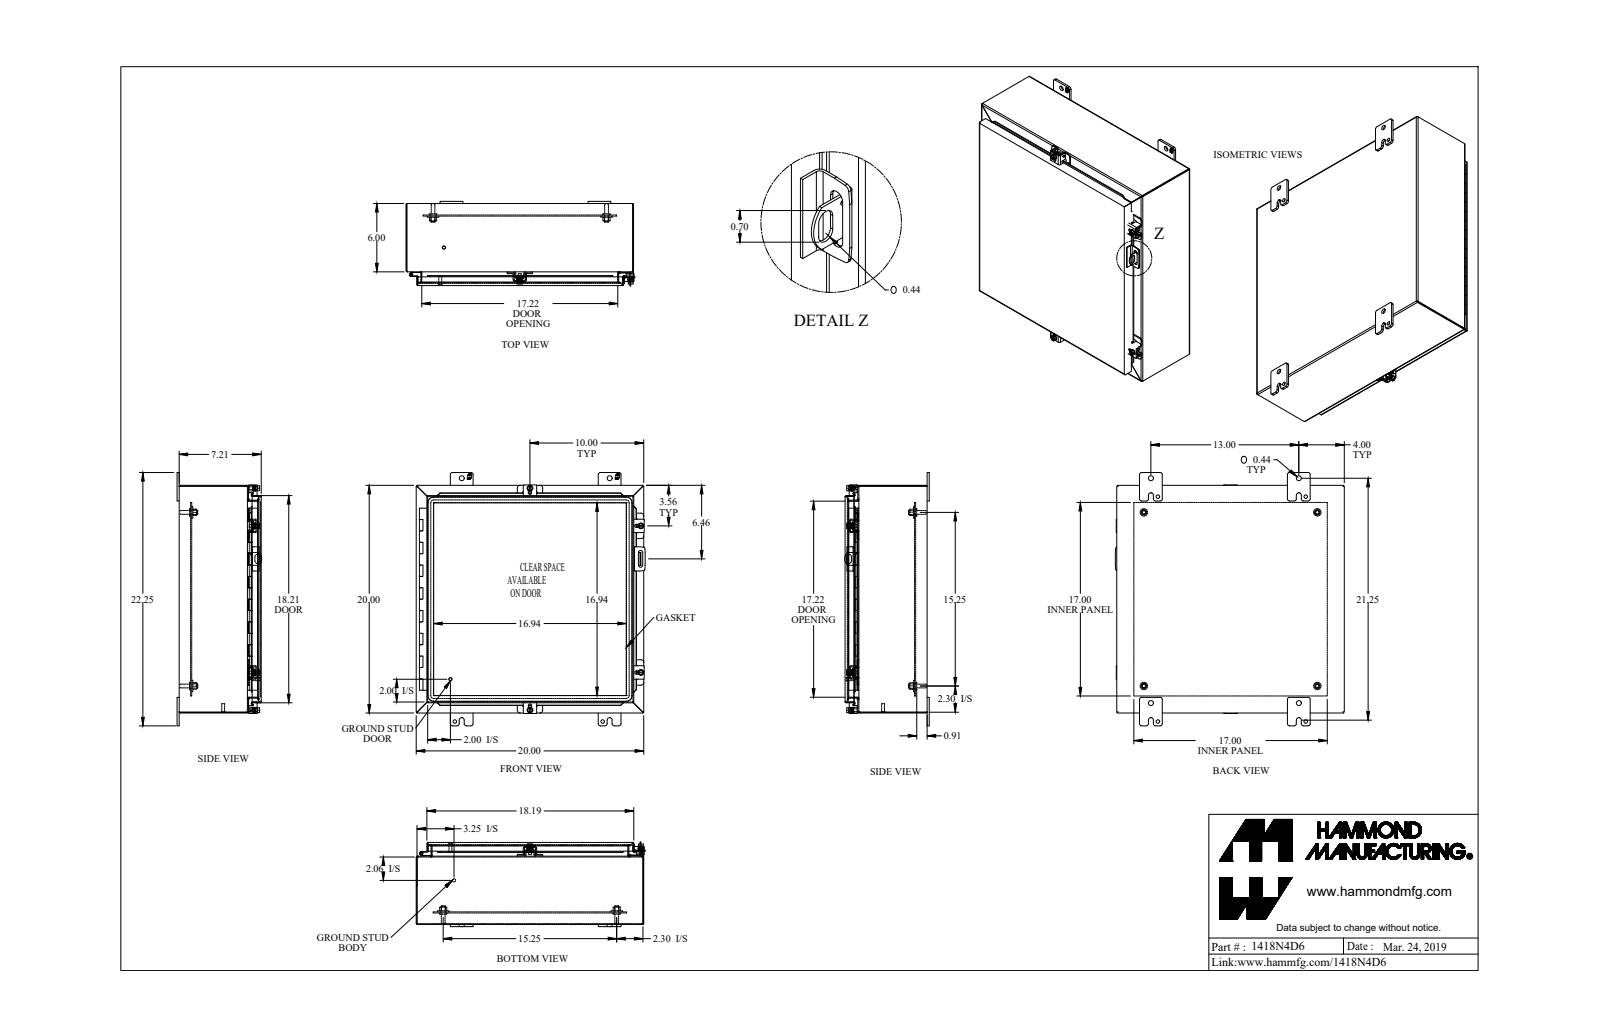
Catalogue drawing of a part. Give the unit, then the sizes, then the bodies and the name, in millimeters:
Units: millimetres
Overall size (bounding box): 565.2 × 511.2 × 188.9
Round holes (diameter × count): ⌀5.4 ×4, ⌀6.7 ×4, ⌀8 ×4, ⌀9.5 ×4, ⌀11.1 ×4, ⌀12.7 ×4, ⌀7.8 ×2, ⌀11.3 ×2, ⌀3.2 ×1, ⌀4.7 ×1
Round bosses / shafts (diameter × count): ⌀16.5 ×4, ⌀12.7 ×4, ⌀9.9 ×4, ⌀9.5 ×4, ⌀8.4 ×4, ⌀6.2 ×4, ⌀25.4 ×2, ⌀7.1 ×2
Partial cylindrical surfaces — rounded edges, fillets, slot ends (radius × count): R4.8 ×26, R0.9 ×24, R2.7 ×24, R1.2 ×21, R3.6 ×21, R6.4 ×20, R1.1 ×8, R3.2 ×8
Main face-to-face distances: 1.8, 506.2, 179.5, 181.3, 1.8, 181.3, 183.1, 2.4, 155.1, 153.3
Hole centre spacings: 387.4, 481.9, 547.8, 201.1, 330.2, 61.8, 201, 387.4
Volume: 2 402 000 mm³ · Surface area: 2 477 000 mm²
Bodies: 39 solids, 1367 faces (833 planar, 450 cylindrical, 84 other)
Part name (STEP PRODUCT): 1418N4D6_Default
STEP written by: SolidWorks 2019 (CONFIG_CONTROL_DESIGN)
